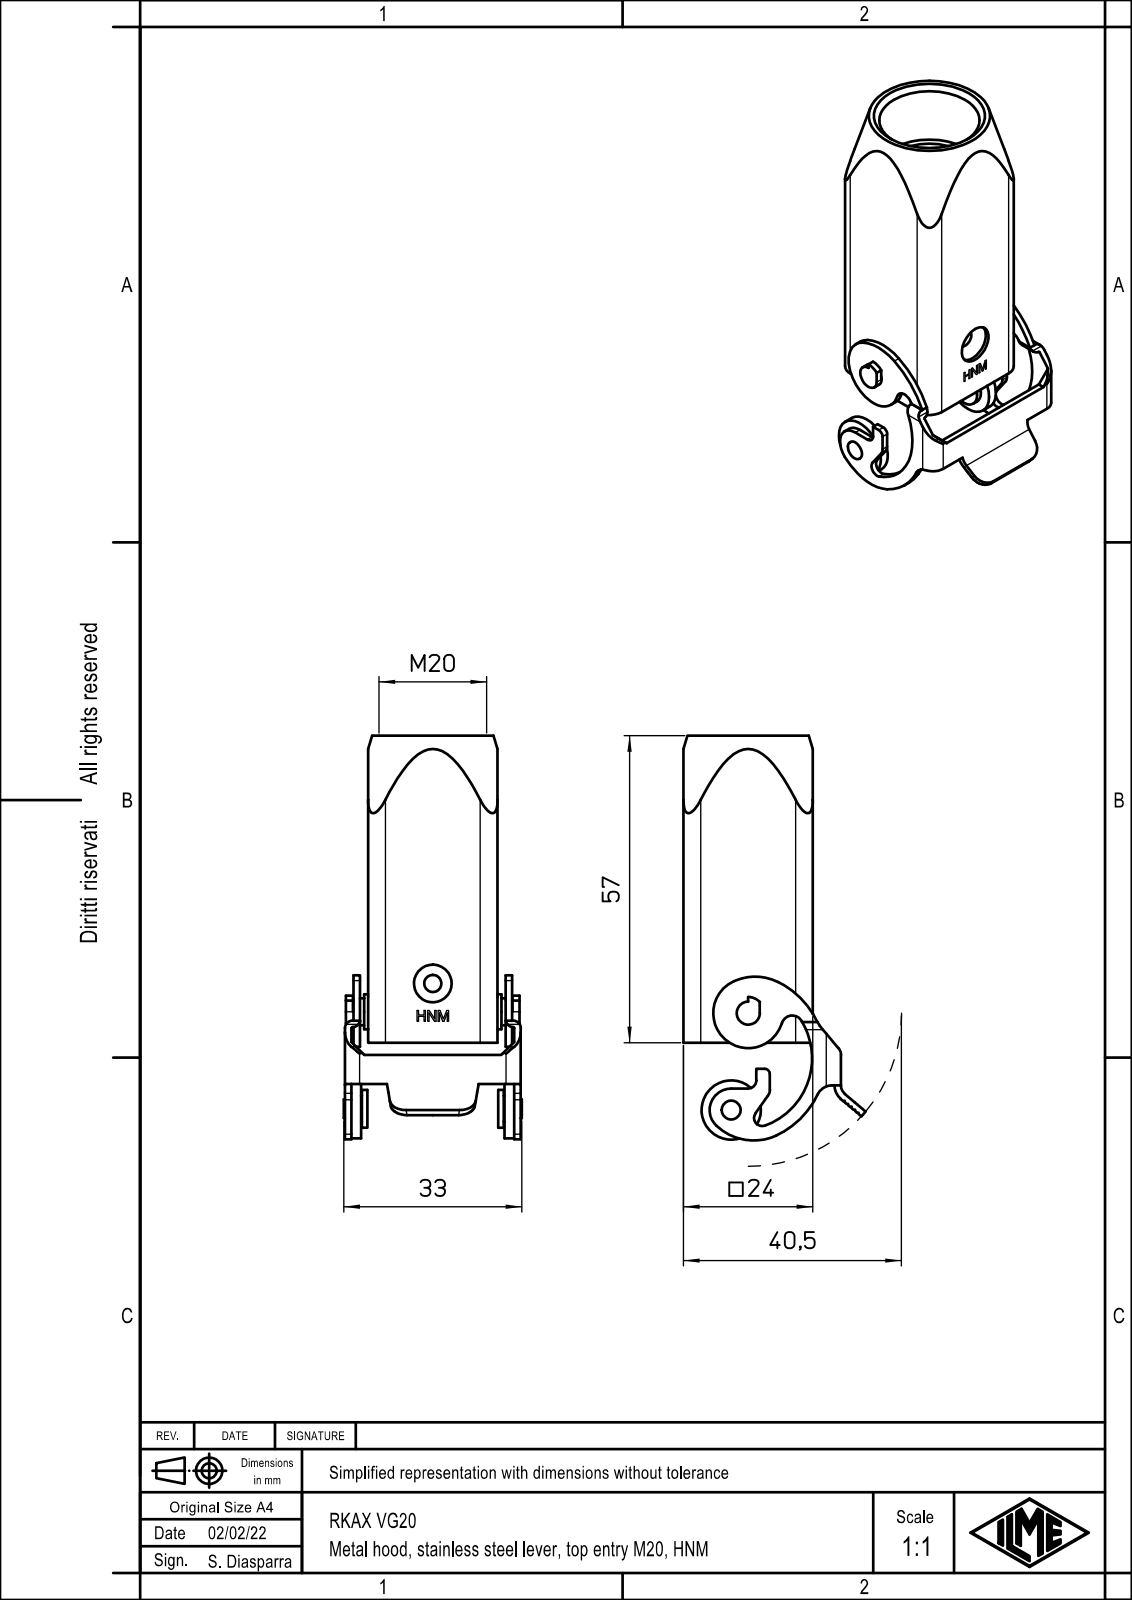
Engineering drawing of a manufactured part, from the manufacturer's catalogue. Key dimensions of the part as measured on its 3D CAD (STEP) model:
Part name (STEP PRODUCT): RKAX_VG20
STEP written by: Creo Elements/Direct Modeling 20.1B 02-Apr-2019 (C) Parametric Technology GmbH (AUTOMOTIVE_DESIGN)
Units: millimetres
Bodies: 1 solid, 247 faces (129 planar, 111 cylindrical, 7 other)
Overall size (bounding box): 75.16 × 33.8 × 33
Volume: 9 911 mm³ · Surface area: 12 839 mm²
Round holes (diameter × count): ⌀3.2 ×1, ⌀7 ×1, ⌀16 ×1, ⌀18.6 ×1
Round bosses / shafts (diameter × count): ⌀11 ×1, ⌀7 ×1, ⌀6 ×1, ⌀5 ×1, ⌀4.8 ×1, ⌀4.3 ×1, ⌀3.5 ×1
Partial cylindrical surfaces — rounded edges, fillets, slot ends (radius × count): R0.25 ×15, R2 ×8, R3.2 ×5, R1.4 ×4, R3 ×4, R0.12 ×3, R0.2 ×2, R1.5 ×2
Main face-to-face distances: 1.2, 22.8, 24, 21.6, 5.2, 28, 25.53, 2.73, 2.7, 25.5
